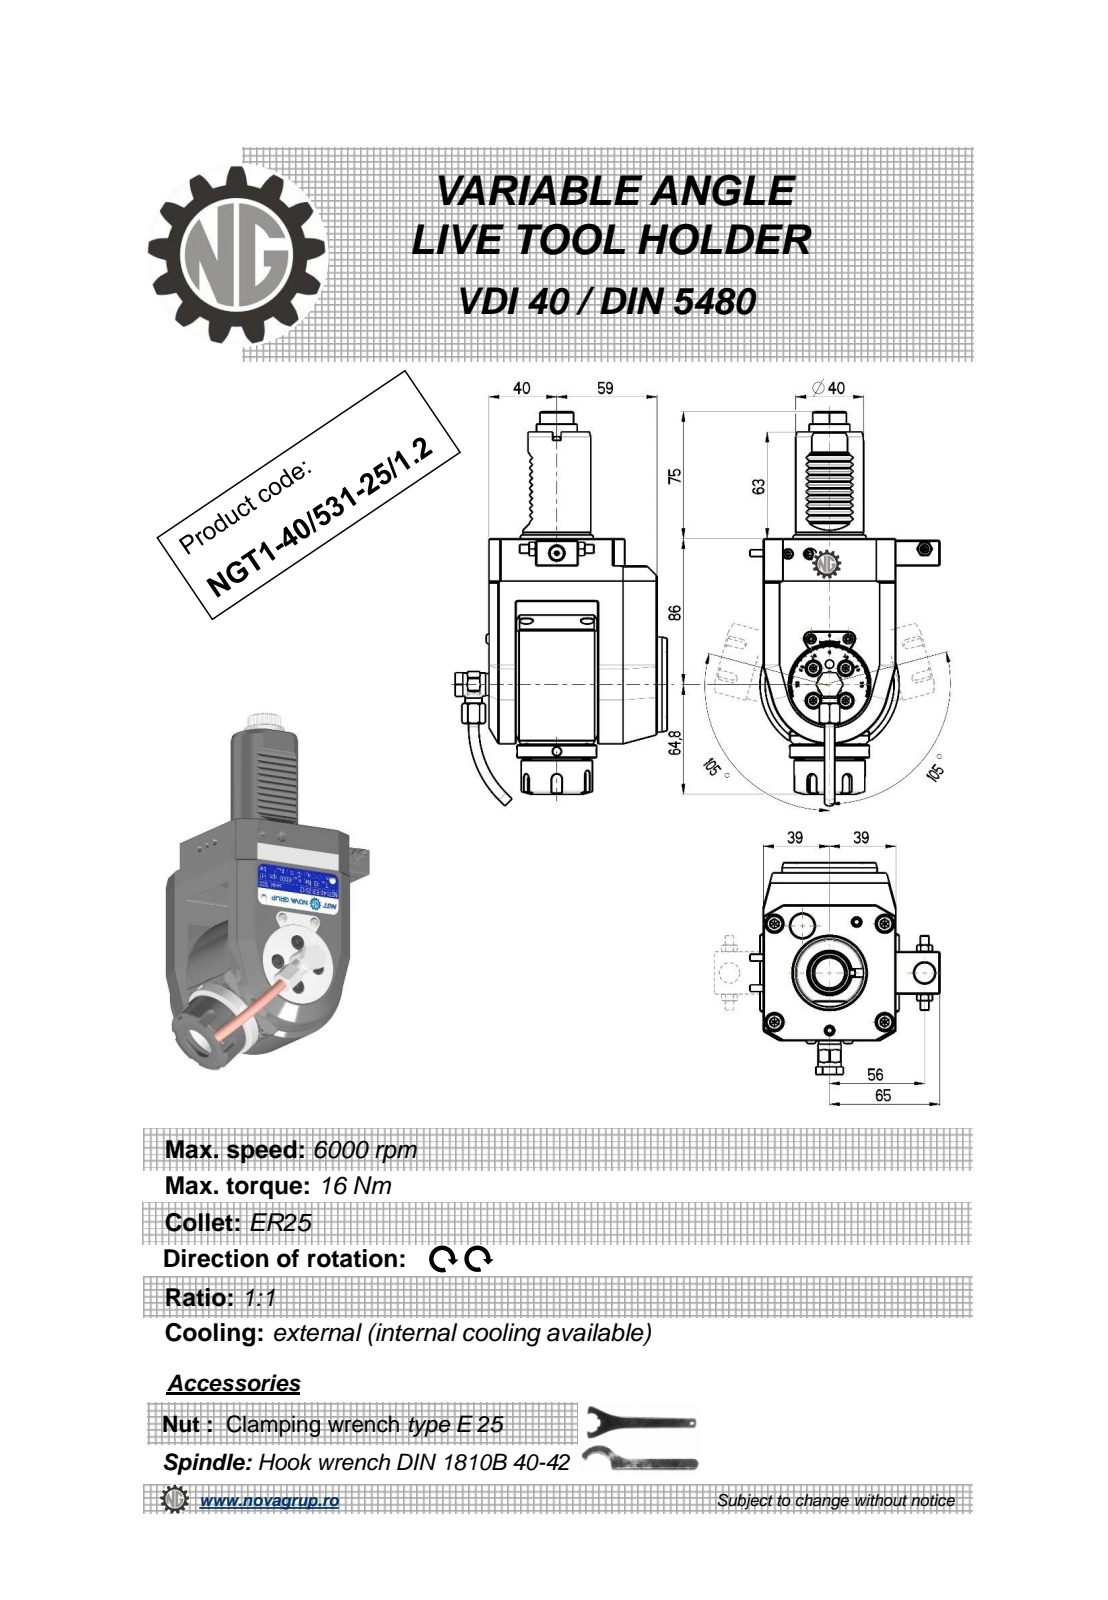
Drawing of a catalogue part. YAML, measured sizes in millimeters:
part_name: "NGT1_40_531_25_1_2"
step_written_by: "PRO/ENGINEER BY PARAMETRIC TECHNOLOGY CORPORATION, 2010280 (CONFIG_CONTROL_DESIGN)"
units: millimeters
bodies: {solids: 1, faces: 699, planar: 248, cylindrical: 235, other: 216}
overall_size: [232.67, 124.9, 106]
volume: 921498
surface_area: 84255
round_holes:
  - {diameter: 4, count: 3}
  - {diameter: 5, count: 2}
  - {diameter: 3, count: 1}
  - {diameter: 4.2, count: 1}
  - {diameter: 6.2, count: 1}
  - {diameter: 9, count: 1}
  - {diameter: 9.5, count: 1}
  - {diameter: 11, count: 1}
  - {diameter: 12, count: 1}
  - {diameter: 20.3, count: 1}
round_bosses_or_shafts:
  - {diameter: 10, count: 2}
  - {diameter: 6, count: 2}
  - {diameter: 5.7, count: 2}
  - {diameter: 82, count: 1}
  - {diameter: 56, count: 1}
  - {diameter: 47, count: 1}
  - {diameter: 42, count: 1}
  - {diameter: 40, count: 1}
partial_cylinders:
  - {radius: 2.08, count: 48}
  - {radius: 0.26, count: 12}
  - {radius: 0.3, count: 10}
  - {radius: 0.16, count: 6}
  - {radius: 3, count: 5}
  - {radius: 0.5, count: 4}
  - {radius: 1, count: 2}
  - {radius: 10, count: 2}
face_to_face_distances: [16, 37, 99, 78, 64, 6, 105, 41, 83, 35]
hole_center_spacings: [0.4, 39.45, 49, 49.4, 56, 74.41, 74.68, 97.65]
